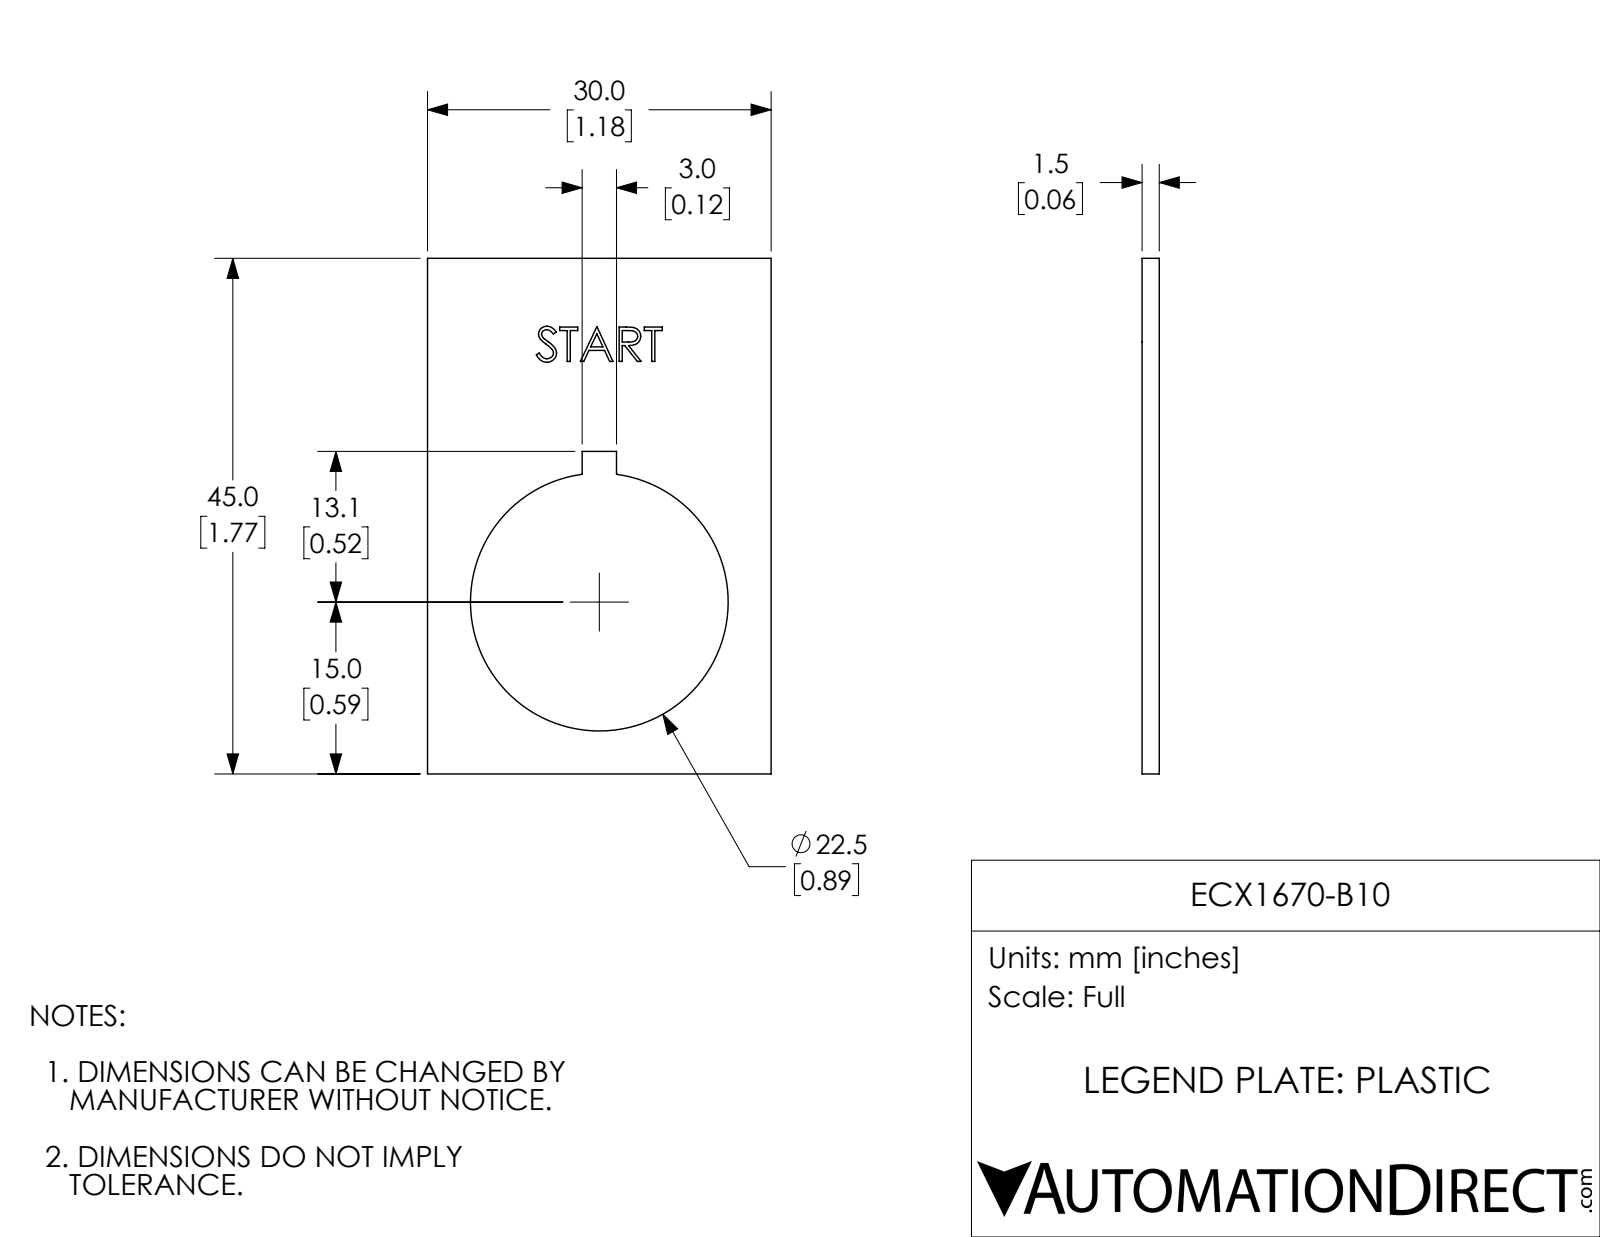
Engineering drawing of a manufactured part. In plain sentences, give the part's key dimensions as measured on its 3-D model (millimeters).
The part is named "ECX1670-B10". Its 3-D file was written by "SolidWorks 2017 (AUTOMOTIVE_DESIGN)". It is 1 solid with 79 faces: 56 planar, 3 cylindrical and 20 other. Overall it measures 45 by 30 by 1.5 millimeters. Its volume is 1 400 cubic millimeters and its surface area 2 232 square millimeters. Round holes: 1 of diameter 22.5. The main face-to-face distances are 1.5, 30, 45, 1.5, 13.5, 16.5, 28.1, 16.8, 3, 7.4.
